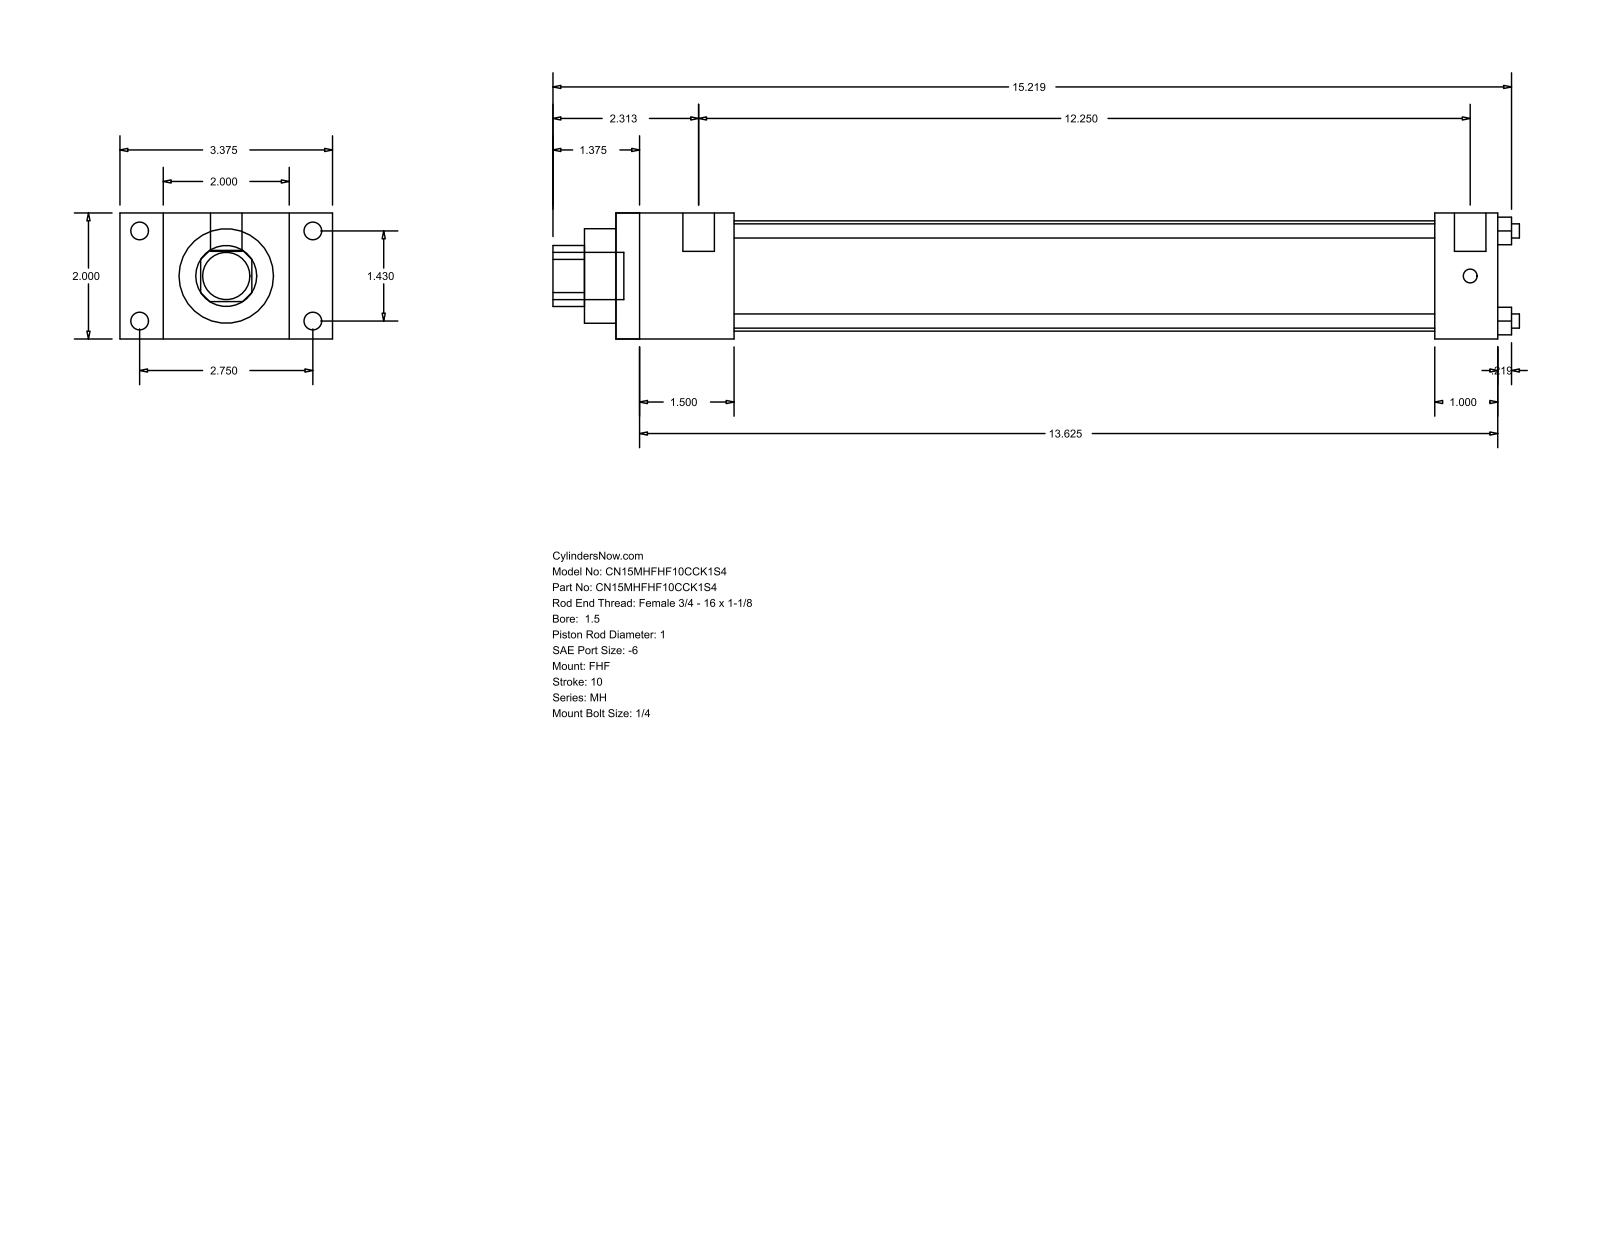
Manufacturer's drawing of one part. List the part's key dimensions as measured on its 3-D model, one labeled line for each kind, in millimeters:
Part name (STEP PRODUCT): MH_FHF__0150_1
STEP written by: GSSL Pune (CONFIG_CONTROL_DESIGN)
Units: millimetres
Bodies: 0 solids, 88 faces (60 planar, 28 cylindrical, 0 other)
Overall size (bounding box): 389.73 × 85.72 × 50.8
Round holes (diameter × count): ⌀5.71 ×4, ⌀25.4 ×1, ⌀38.1 ×1, ⌀44.45 ×1
Round bosses / shafts (diameter × count): ⌀7.14 ×4, ⌀5.56 ×4, ⌀12.7 ×2, ⌀19.05 ×1
Partial cylindrical surfaces — rounded edges, fillets, slot ends (radius × count): R12.29 ×1
Main face-to-face distances: 50.8, 17.46, 68.26, 47.63, 85.72, 355.6, 307.97, 25.4, 330.2, 282.57
Hole centre spacings: 25.68, 36.32, 51.36
